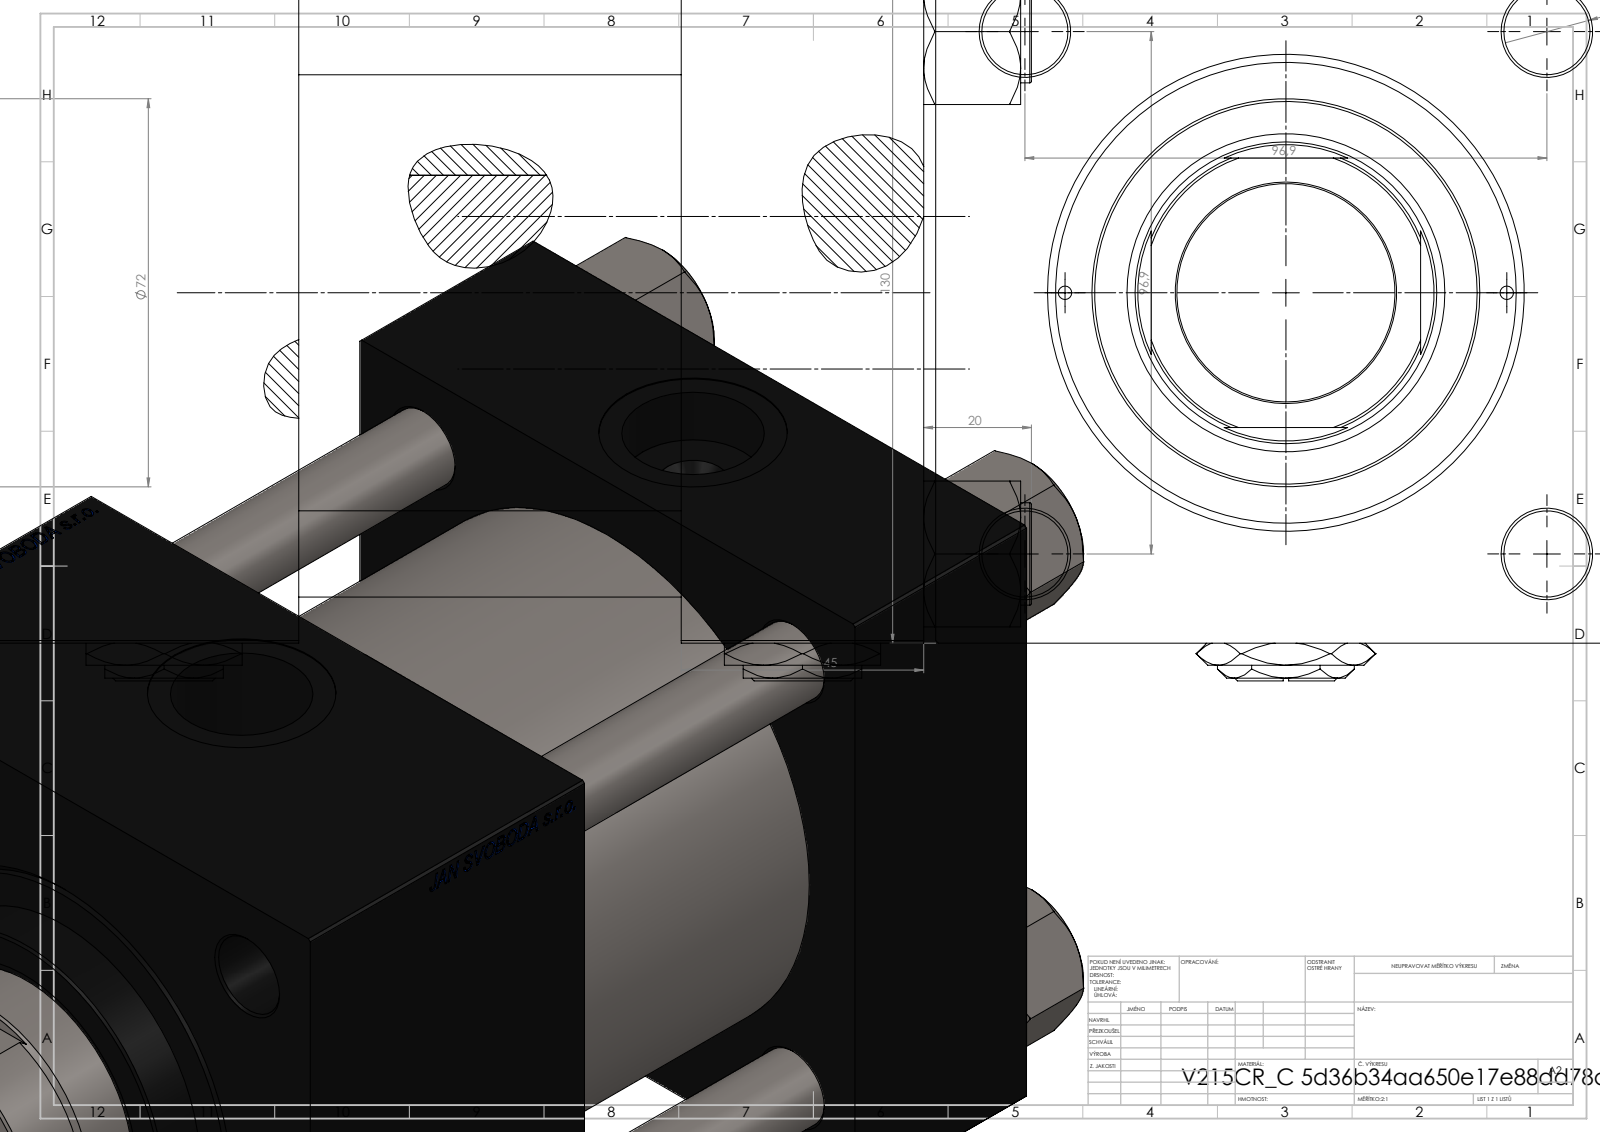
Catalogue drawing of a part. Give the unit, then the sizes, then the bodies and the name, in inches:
Units: inches
Overall size (bounding box): 9.567 × 5.394 × 5.118
Round holes (diameter × count): ⌀0.63 ×4, ⌀0.098 ×2, ⌀0.276 ×2, ⌀1.041 ×2, ⌀1.378 ×2, ⌀1.594 ×1, ⌀2.205 ×1, ⌀2.323 ×1, ⌀2.992 ×1, ⌀3.366 ×1, ⌀3.937 ×1
Round bosses / shafts (diameter × count): ⌀0.748 ×4, ⌀4.173 ×1, ⌀2.835 ×1
Partial cylindrical surfaces — rounded edges, fillets, slot ends (radius × count): R1.063 ×1
Main face-to-face distances: 5.118, 1.772, 7.402, 5.63, 4.567, 2.795, 2.835, 0.787, 2.008, 3.622
Hole centre spacings: 1.93, 2.698, 3.815, 4.005, 1.614, 5.395, 3.228, 4.665
Volume: 150.1 in³ · Surface area: 528 in²
Bodies: 13 solids, 1303 faces (623 planar, 102 cylindrical, 578 other)
Part name (STEP PRODUCT): Zatka_pro_OIL_PORT; V215_VC_A; V215CR_C_TYCINKA; NUT_M5_C (+2 more)
STEP written by: SolidWorks 2019 (CONFIG_CONTROL_DESIGN)
